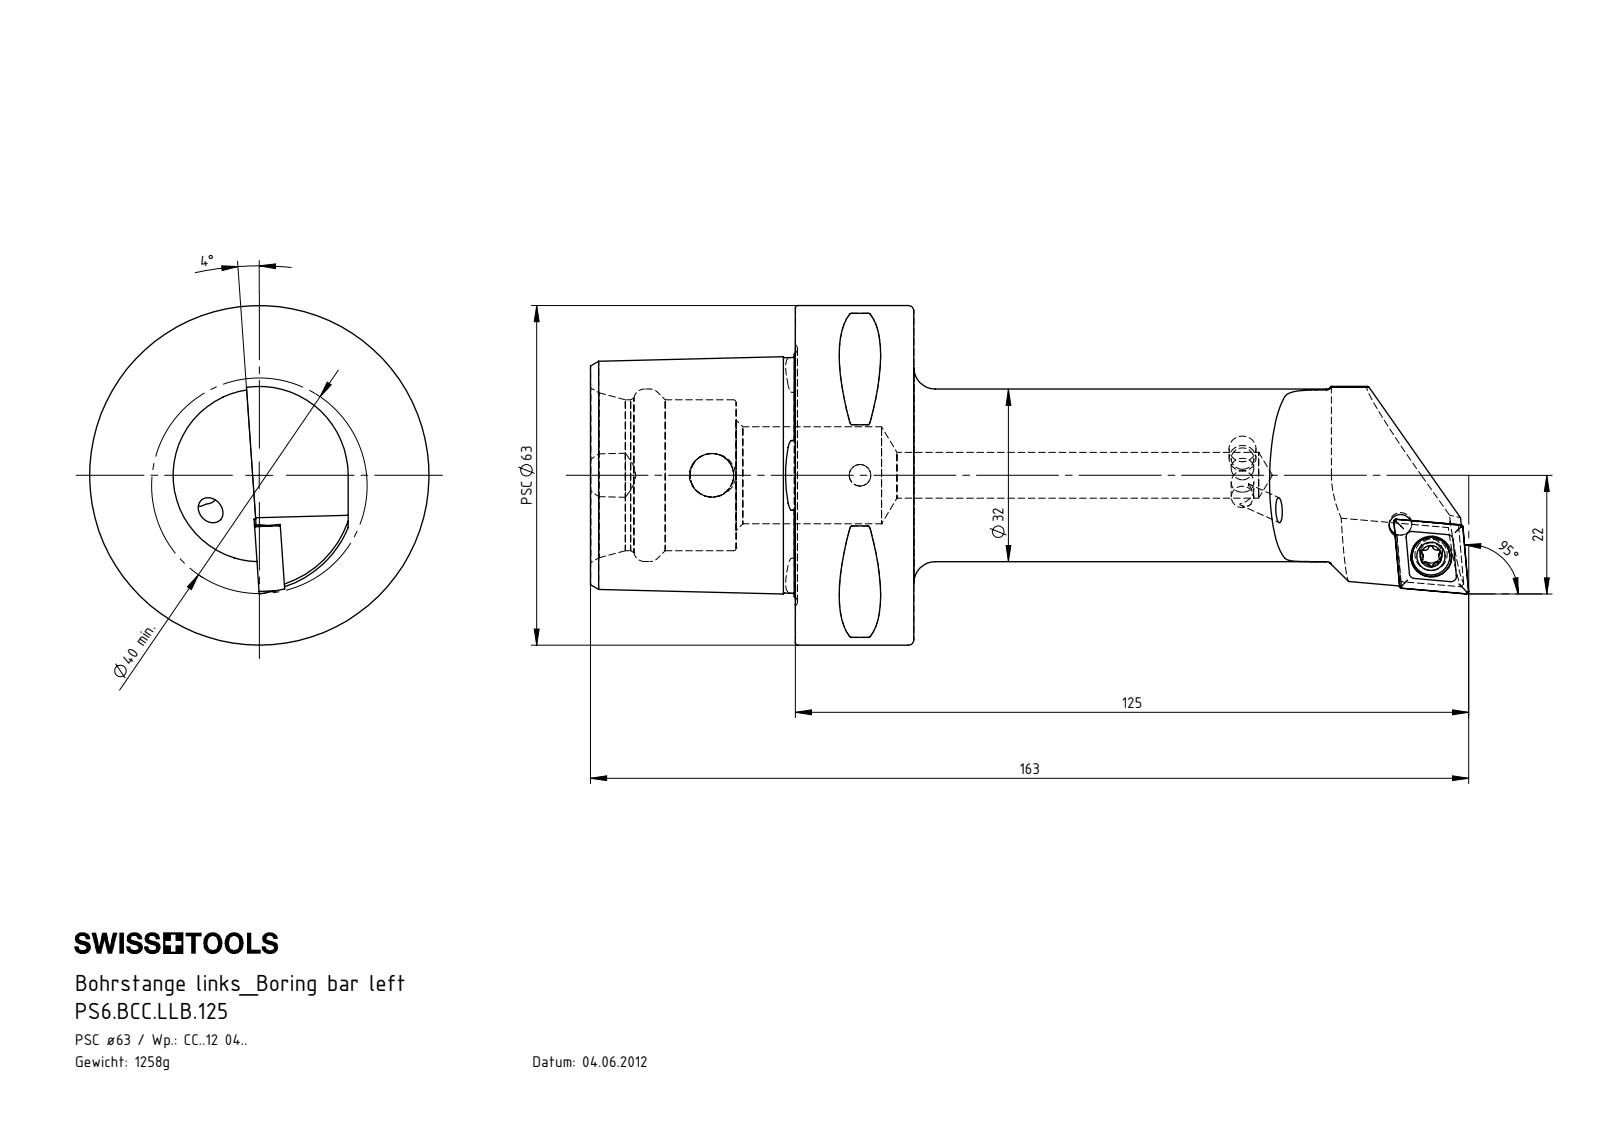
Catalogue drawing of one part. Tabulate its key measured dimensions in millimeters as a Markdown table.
| quantity | value |
| --- | --- |
| part name | PS6-BCC.LLB.125; KVT_MB_600_050; WCC-ER2.001.010_A; CCMT120404 (+1 more) |
| STEP written by | SolidWorks 2012 (CONFIG_CONTROL_DESIGN) |
| units | millimeters |
| bodies | 5 solids, 281 faces (49 planar, 75 cylindrical, 157 other) |
| overall size | 163 × 63 × 63 |
| volume | 161 236 mm³ |
| surface area | 32 477 mm² |
| round holes (diameter × count) | 4.2 × 4, 4 × 2, 5.5 × 1, 7.6 × 1, 8.1 × 1, 8.5 × 1, 18 × 1, 28 × 1, 32 × 1 |
| round bosses / shafts (diameter × count) | 5 × 2, 63 × 1, 7 × 1 |
| partial cylindrical surfaces (radius × count) | 0.5 × 8, 0.39 × 6, 0.69 × 6, 3 × 1, 6 × 1, 16.5 × 1, 19 × 1 |
| main face-to-face distances | 22, 38, 60, 24.88, 27, 11, 33, 4.46, 55.8, 37.8 |
| hole center spacings | 8.01, 8.09, 27.5 |
